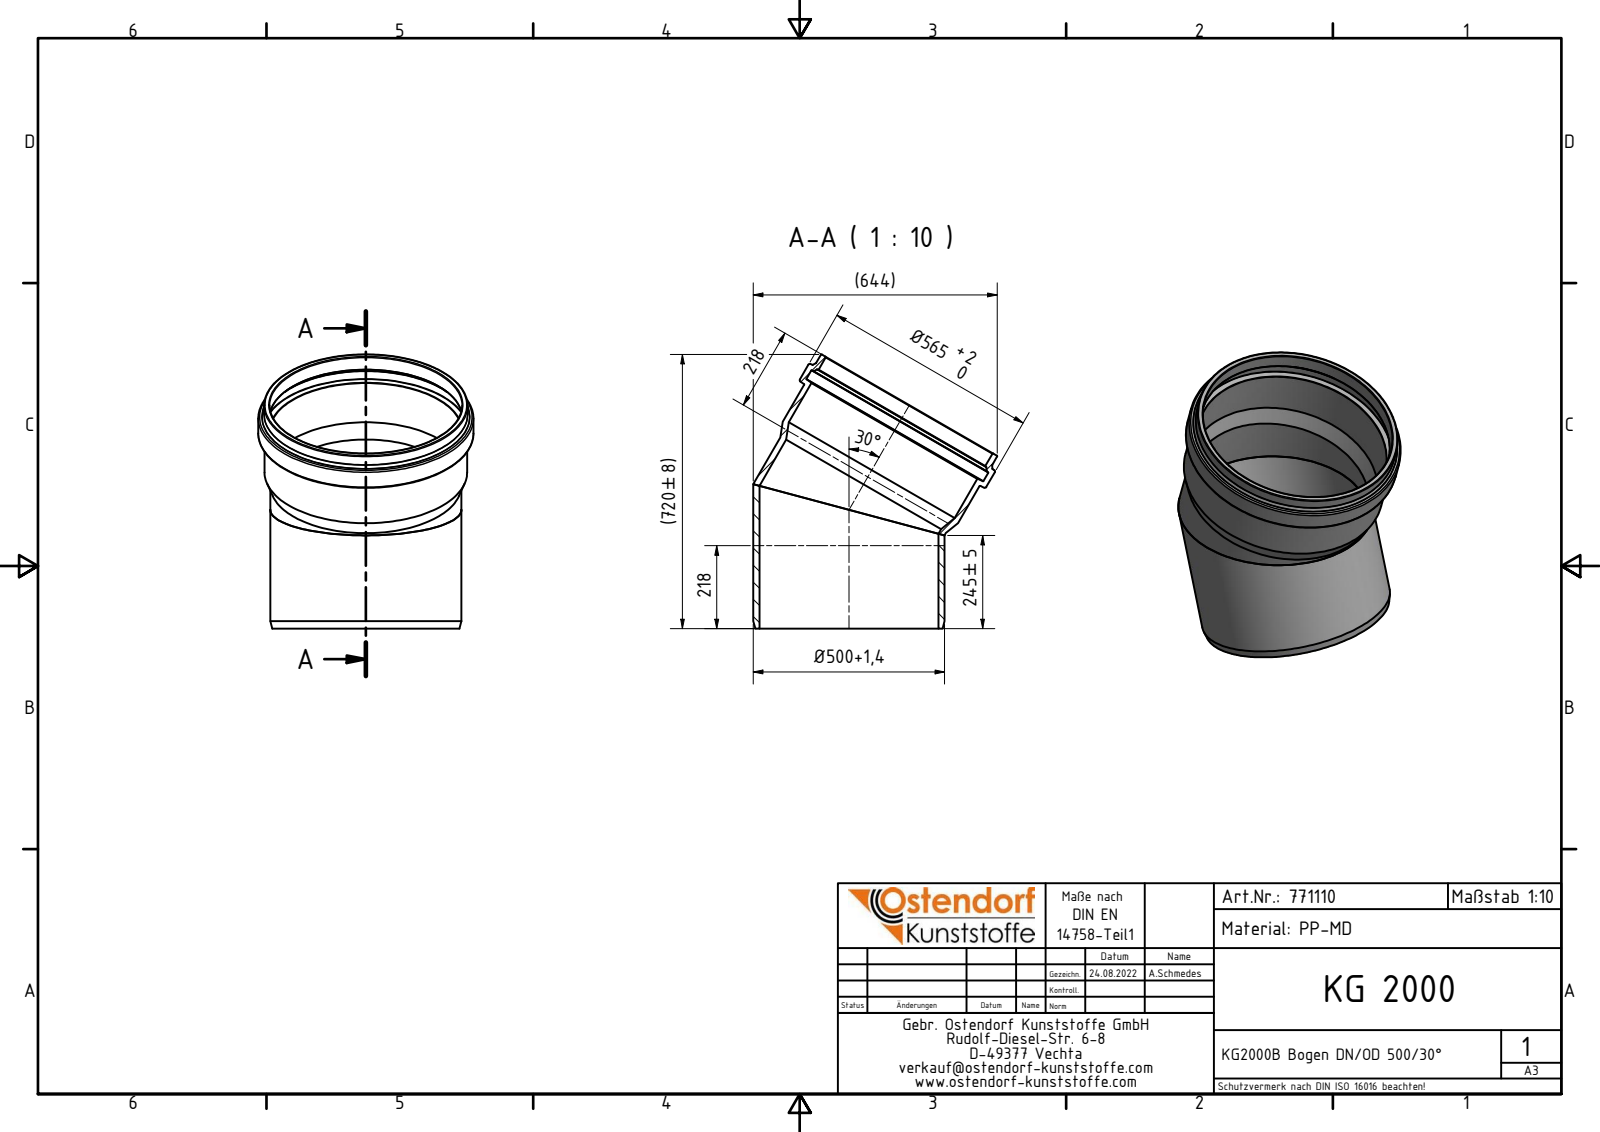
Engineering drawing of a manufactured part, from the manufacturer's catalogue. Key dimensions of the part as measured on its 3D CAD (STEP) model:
Part name (STEP PRODUCT): 771110 KG2000B Bogen DN_OD 500x30°; 771110 KG2000B Bogen DN_OD 500x30° Teil 1; 771110 KG2000B Bogen DN_OD 500x30° Teil 2
STEP written by: Autodesk Inventor 2020 (AUTOMOTIVE_DESIGN)
Units: millimetres
Bodies: 2 solids, 37 faces (4 planar, 10 cylindrical, 23 other)
Overall size (bounding box): 710.5 × 651.36 × 565
Volume: 15 870 000 mm³ · Surface area: 2 151 000 mm²
Round holes (diameter × count): ⌀470 ×2, ⌀502.98 ×1, ⌀505.34 ×1, ⌀536.68 ×1
Round bosses / shafts (diameter × count): ⌀502 ×2, ⌀565 ×1, ⌀534.22 ×1, ⌀531.86 ×1
